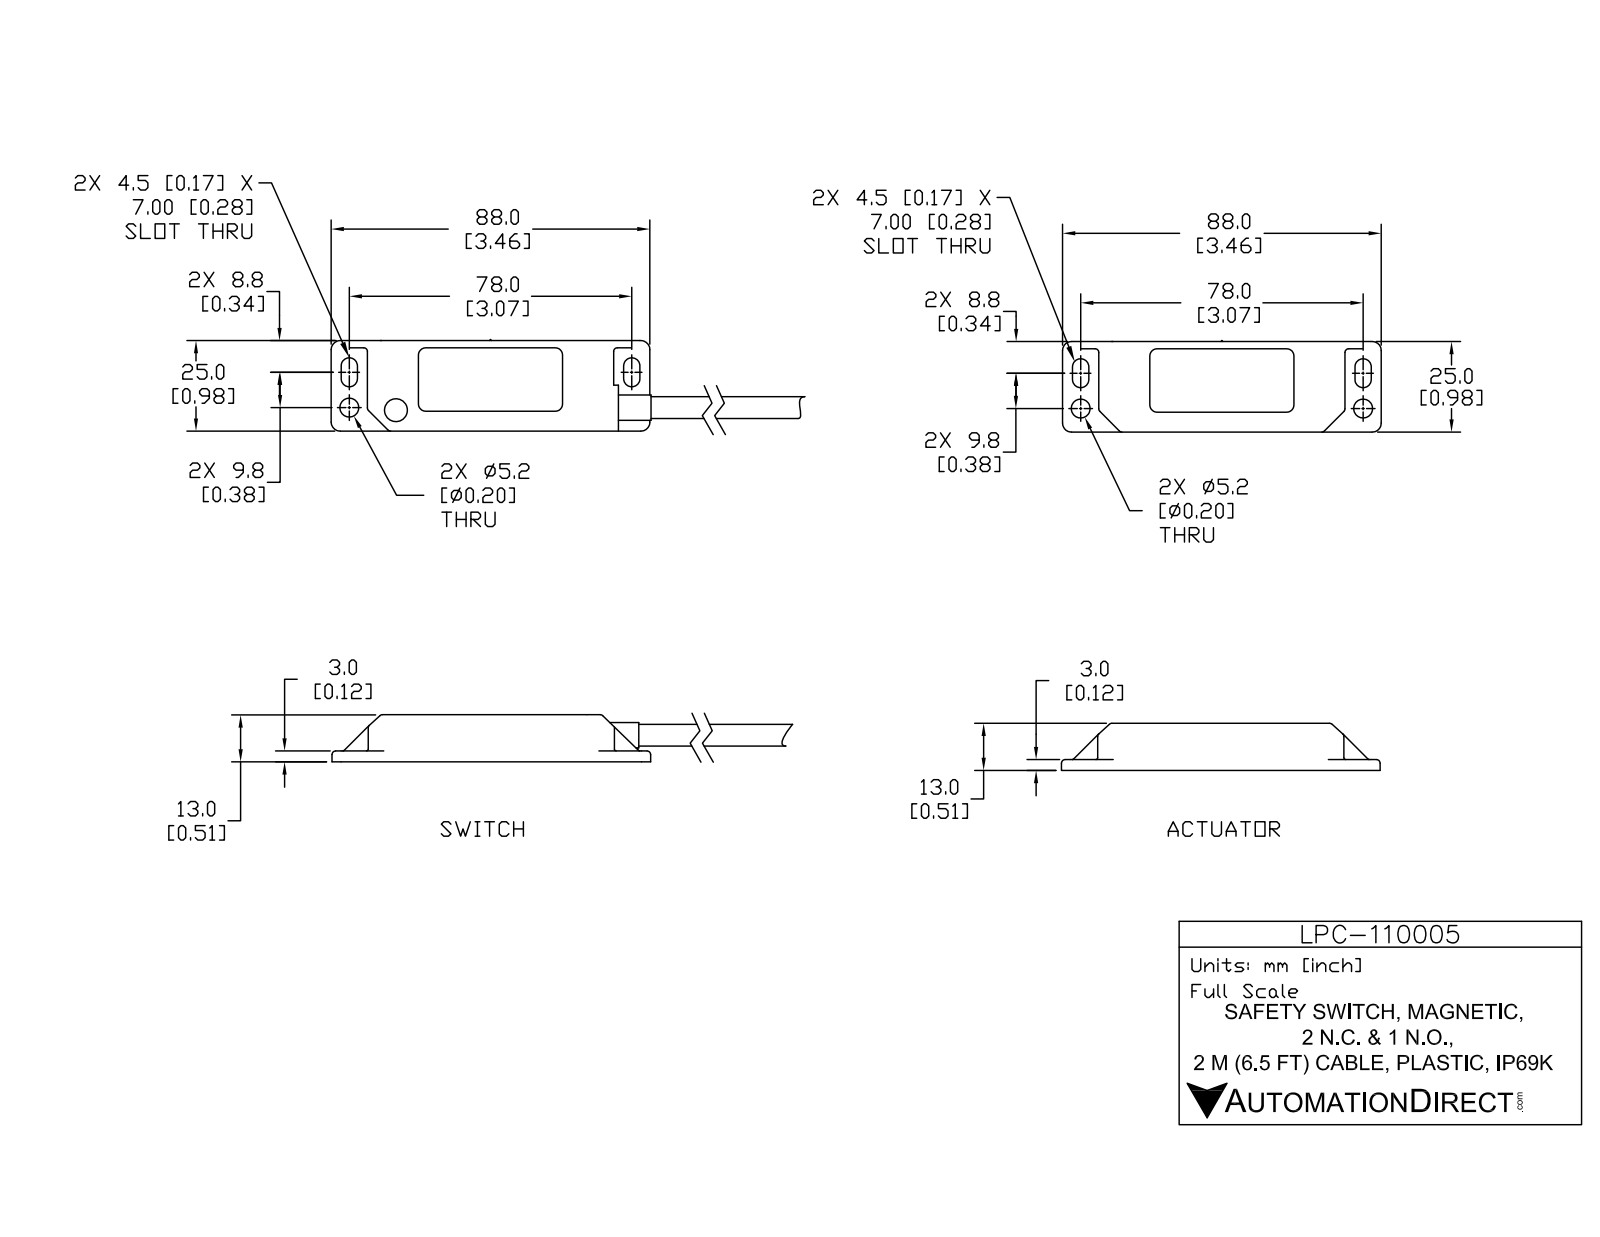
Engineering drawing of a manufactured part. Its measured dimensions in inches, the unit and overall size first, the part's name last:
Units: inches
Overall size (bounding box): 10.221 × 1.992 × 0.543
Round holes (diameter × count): ⌀0.197 ×4, ⌀0.205 ×4, ⌀0.119 ×1, ⌀0.173 ×1, ⌀0.213 ×1, ⌀0.232 ×1, ⌀0.276 ×1
Round bosses / shafts (diameter × count): ⌀0.079 ×4, ⌀0.193 ×2, ⌀0.091 ×2, ⌀0.339 ×1, ⌀0.299 ×1, ⌀0.28 ×1, ⌀0.236 ×1, ⌀0.209 ×1
Partial cylindrical surfaces — rounded edges, fillets, slot ends (radius × count): R0.02 ×116, R0.039 ×49, R0.079 ×10, R0.089 ×8, R0.098 ×8, R0.012 ×6, R0.189 ×1
Main face-to-face distances: 0.067, 0.441, 0.079, 0.374, 0.059, 0.071, 0.508, 0.445, 0.512, 0.988
Hole centre spacings: 0.748, 1.097, 1.19, 1.275, 1.48, 1.571, 1.784, 1.895
Volume: 1.698 in³ · Surface area: 47.9 in²
Bodies: 11 solids, 1058 faces (401 planar, 303 cylindrical, 354 other)
Part name (STEP PRODUCT): LPC-110005_1; LPC-110005_2; LPC-110005
STEP written by: SolidWorks 2017 (AUTOMOTIVE_DESIGN)
